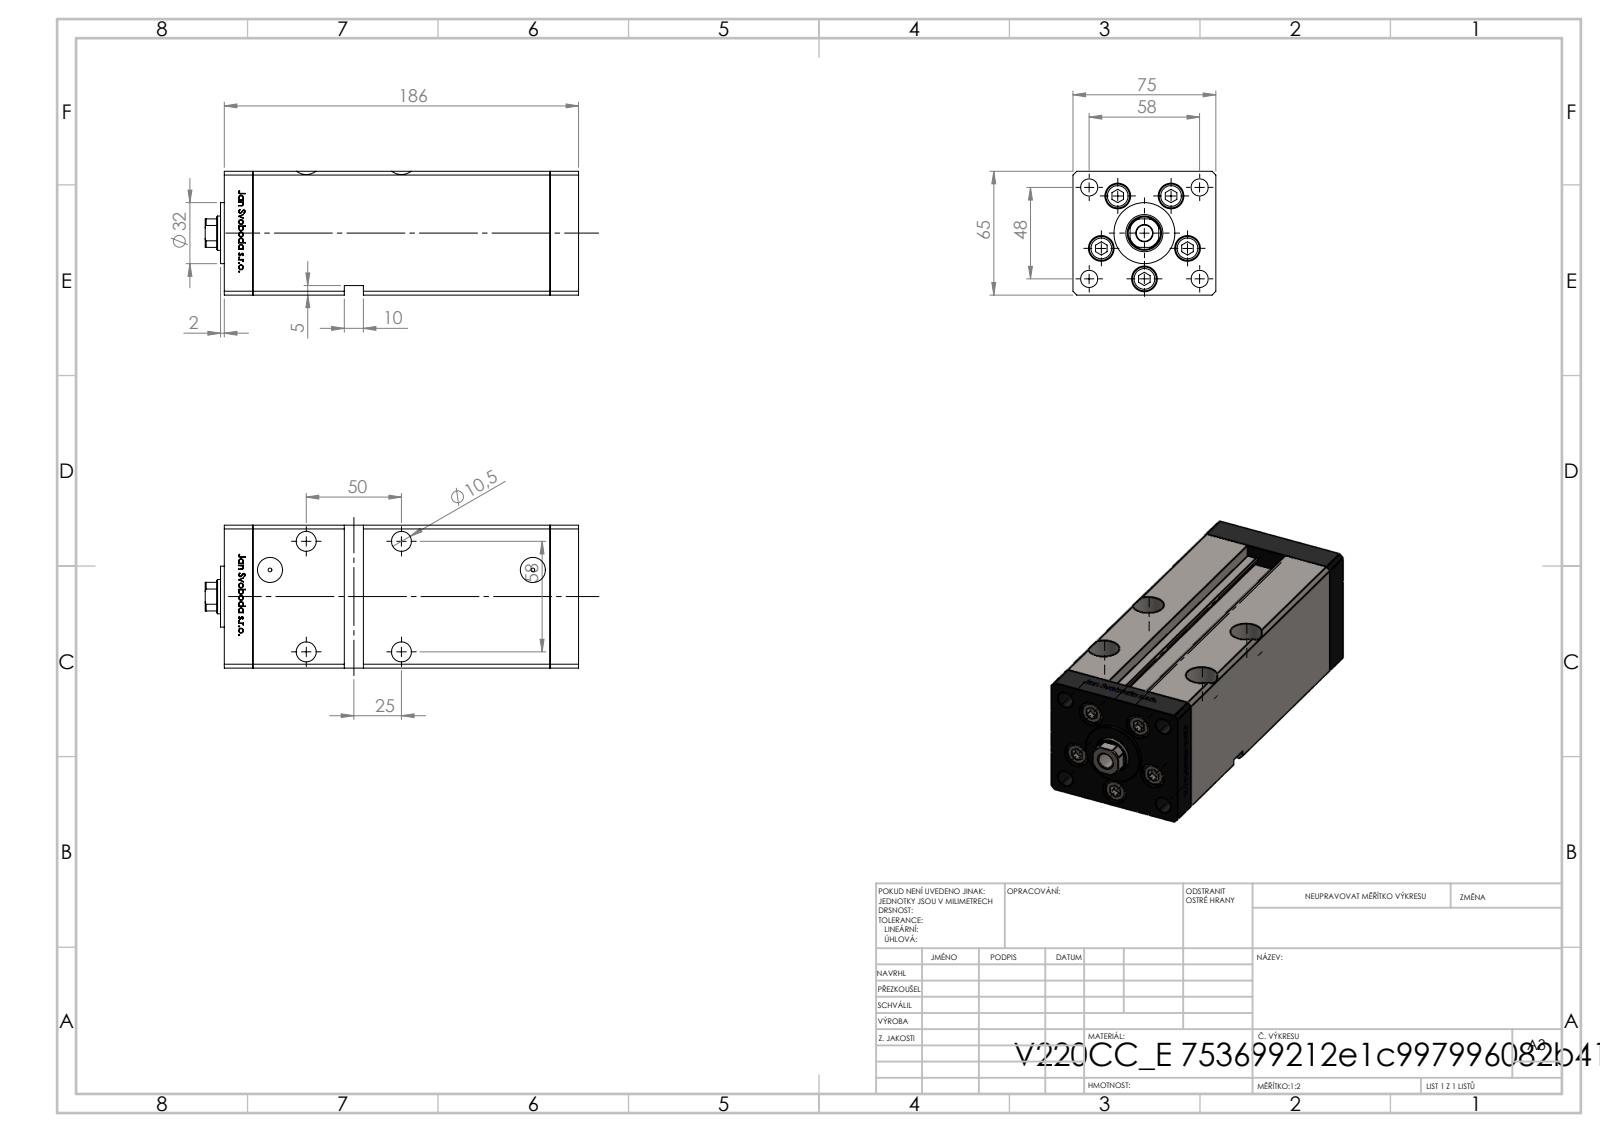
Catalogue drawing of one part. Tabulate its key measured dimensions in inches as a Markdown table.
| quantity | value |
| --- | --- |
| part name | V220C_VC_E; V220C BACK_E; V220C_E MIDDLE; V220C_FRONT_E (+1 more) |
| STEP written by | SolidWorks 2019 (CONFIG_CONTROL_DESIGN) |
| units | inches |
| bodies | 14 solids, 1212 faces (473 planar, 165 cylindrical, 574 other) |
| overall size | 7.717 × 2.953 × 2.559 |
| volume | 46.96 in³ |
| surface area | 227.3 in² |
| round holes (diameter × count) | 0.354 × 9, 0.531 × 5, 0.413 × 4, 0.65 × 4, 0.079 × 2, 0.518 × 2, 0.335 × 1, 0.709 × 1, 0.768 × 1 |
| round bosses / shafts (diameter × count) | 0.492 × 5, 0.315 × 5, 1.26 × 1 |
| partial cylindrical surfaces (radius × count) | 0.037 × 2, 0.335 × 1 |
| main face-to-face distances | 2.953, 2.559, 0.591, 6.142, 6.732, 7.323, 1.102, 2.146, 0.413, 1.033 |
| hole center spacings | 0.945, 1.482, 2.283, 0.617, 0.678, 1.091, 1.135, 1.142 |
